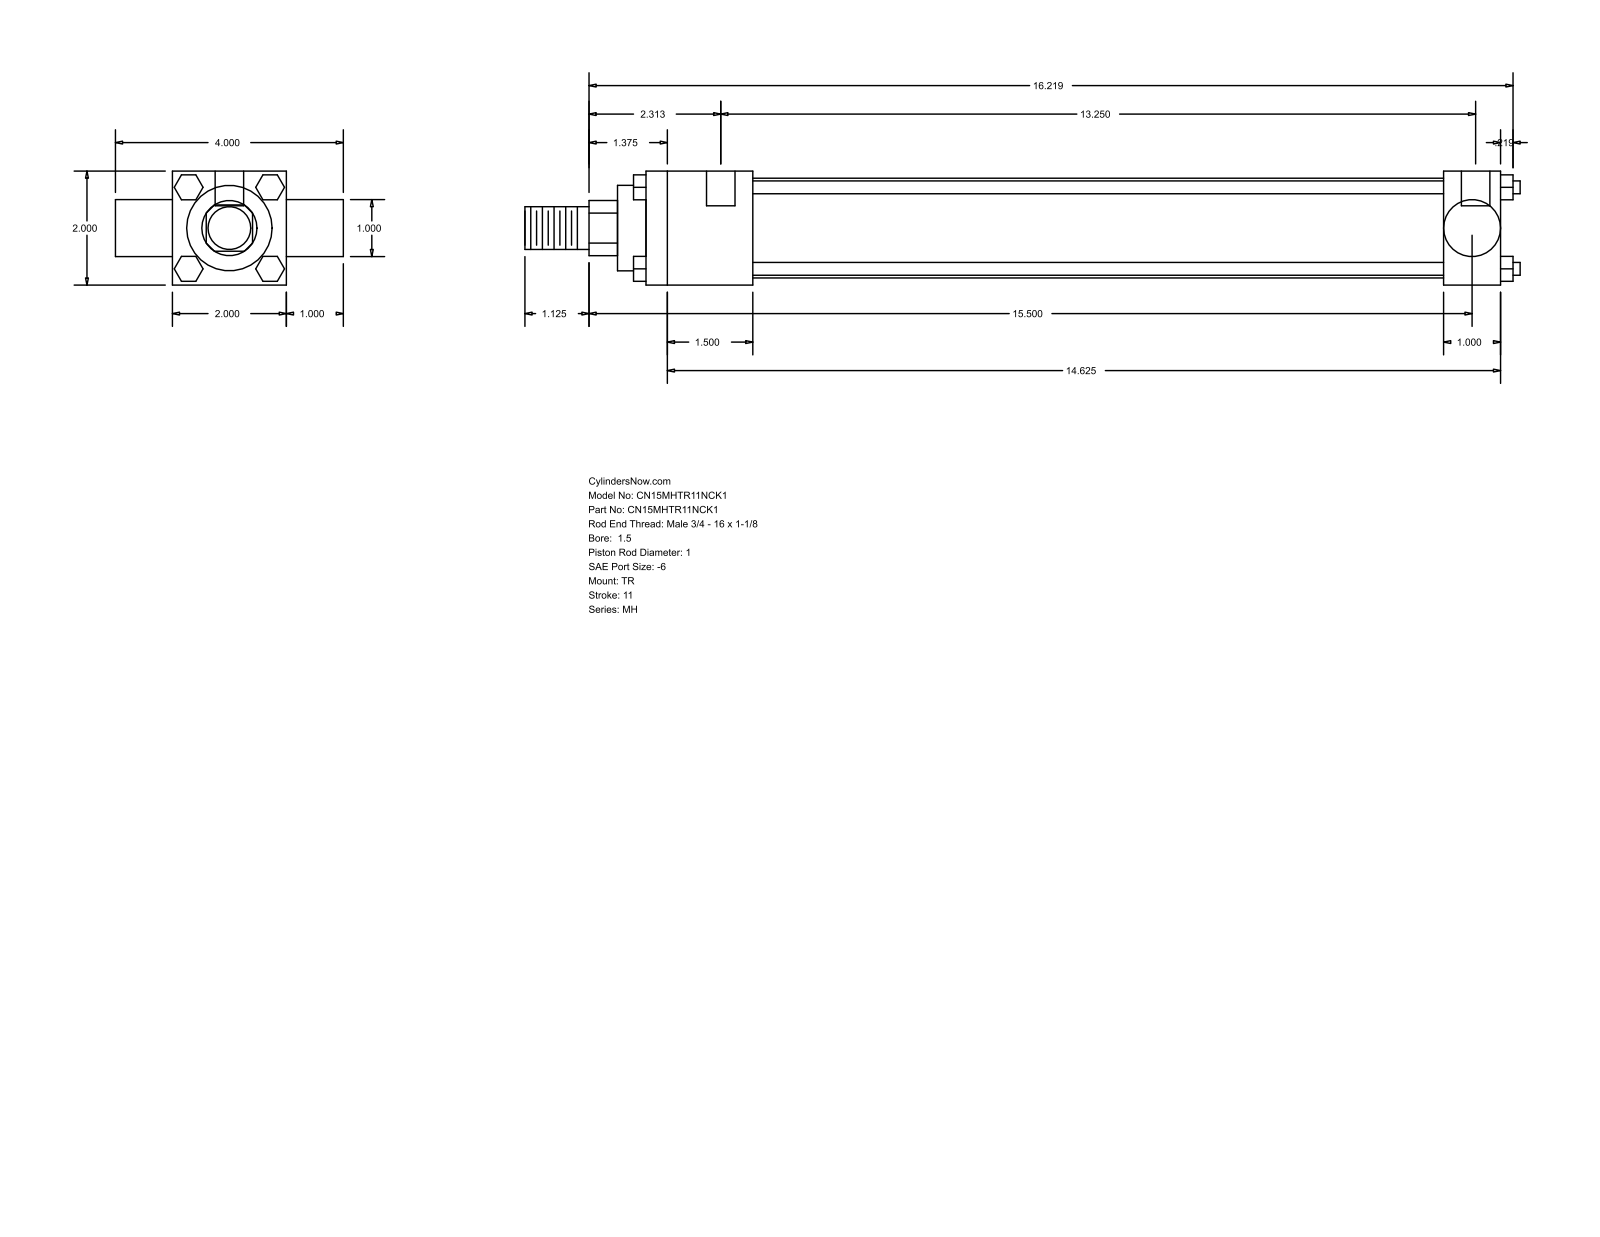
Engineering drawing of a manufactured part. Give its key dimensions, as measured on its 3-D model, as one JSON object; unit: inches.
{"part_name": "MH_TR__0150_1", "step_written_by": "GSSL Pune (CONFIG_CONTROL_DESIGN)", "units": "inches", "bodies": {"solids": 0, "faces": 120, "planar": 92, "cylindrical": 28, "other": 0}, "overall_size": [17.469, 4, 2], "round_holes": [[0.219, 3], [0.5, 2]], "round_bosses_or_shafts": [[0.225, 4], [1.75, 1], [1.5, 1], [1, 1], [0.998, 1], [0.75, 1]], "partial_cylinders_radius": [[0.484, 1]], "face_to_face_distances": [2, 1, 15, 3, 1.875, 13.125, 14, 12.125, 4, 0.5], "hole_center_spacings": [0.125, 13.25, 13.375]}
